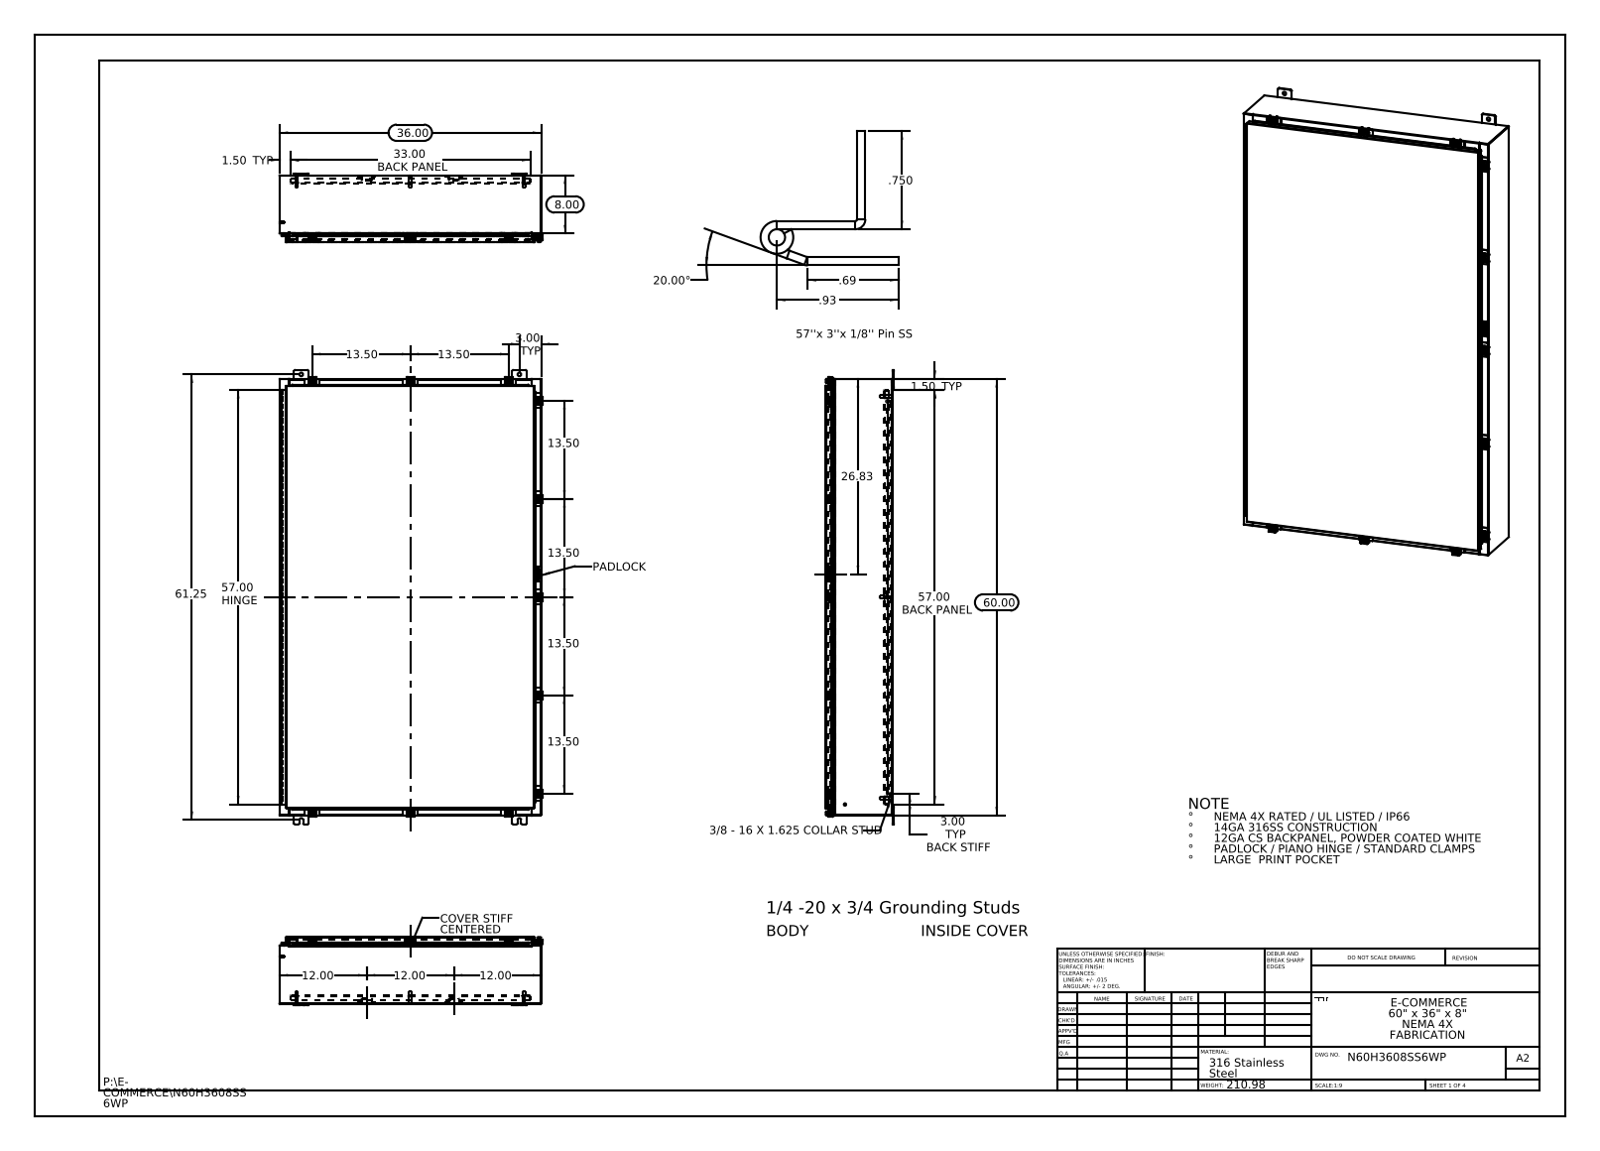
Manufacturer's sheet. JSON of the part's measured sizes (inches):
{"part_name": "N60H3608SS6WP Mounting Feet; N60H3608SS6WP Padlock Hasp; N60H3608SS6WP Standard Clamps; N60H3608SS6WP (+8 more)", "step_written_by": "SolidWorks 2013 (CONFIG_CONTROL_DESIGN)", "units": "inches", "bodies": {"solids": 89, "faces": 3554, "planar": 1796, "cylindrical": 1506, "other": 252}, "overall_size": [62.5, 36.211, 9.389], "volume_in3": 738.9, "surface_area_in2": 18321, "round_holes": [[0.5, 12], [0.213, 11], [0.26, 11], [0.25, 8], [0.125, 2], [0.125, 1]], "round_bosses_or_shafts": [[0.25, 12], [0.5, 11], [0.399, 11], [0.625, 8], [0.375, 8], [0.33, 8], [0.157, 8], [0.14, 8]], "partial_cylinders_radius": [[0.06, 50], [0.013, 39], [0.088, 33], [0.19, 24], [0.12, 22], [0.141, 22], [0.05, 17], [0.08, 16]], "face_to_face_distances": [0.075, 9.126, 9.051, 0.104, 9.201, 1, 8.126, 1.075, 8.051, 1.179], "hole_center_spacings": [13.5, 13.663, 2.225, 27, 27.625, 29.802, 41.709, 57.39]}
